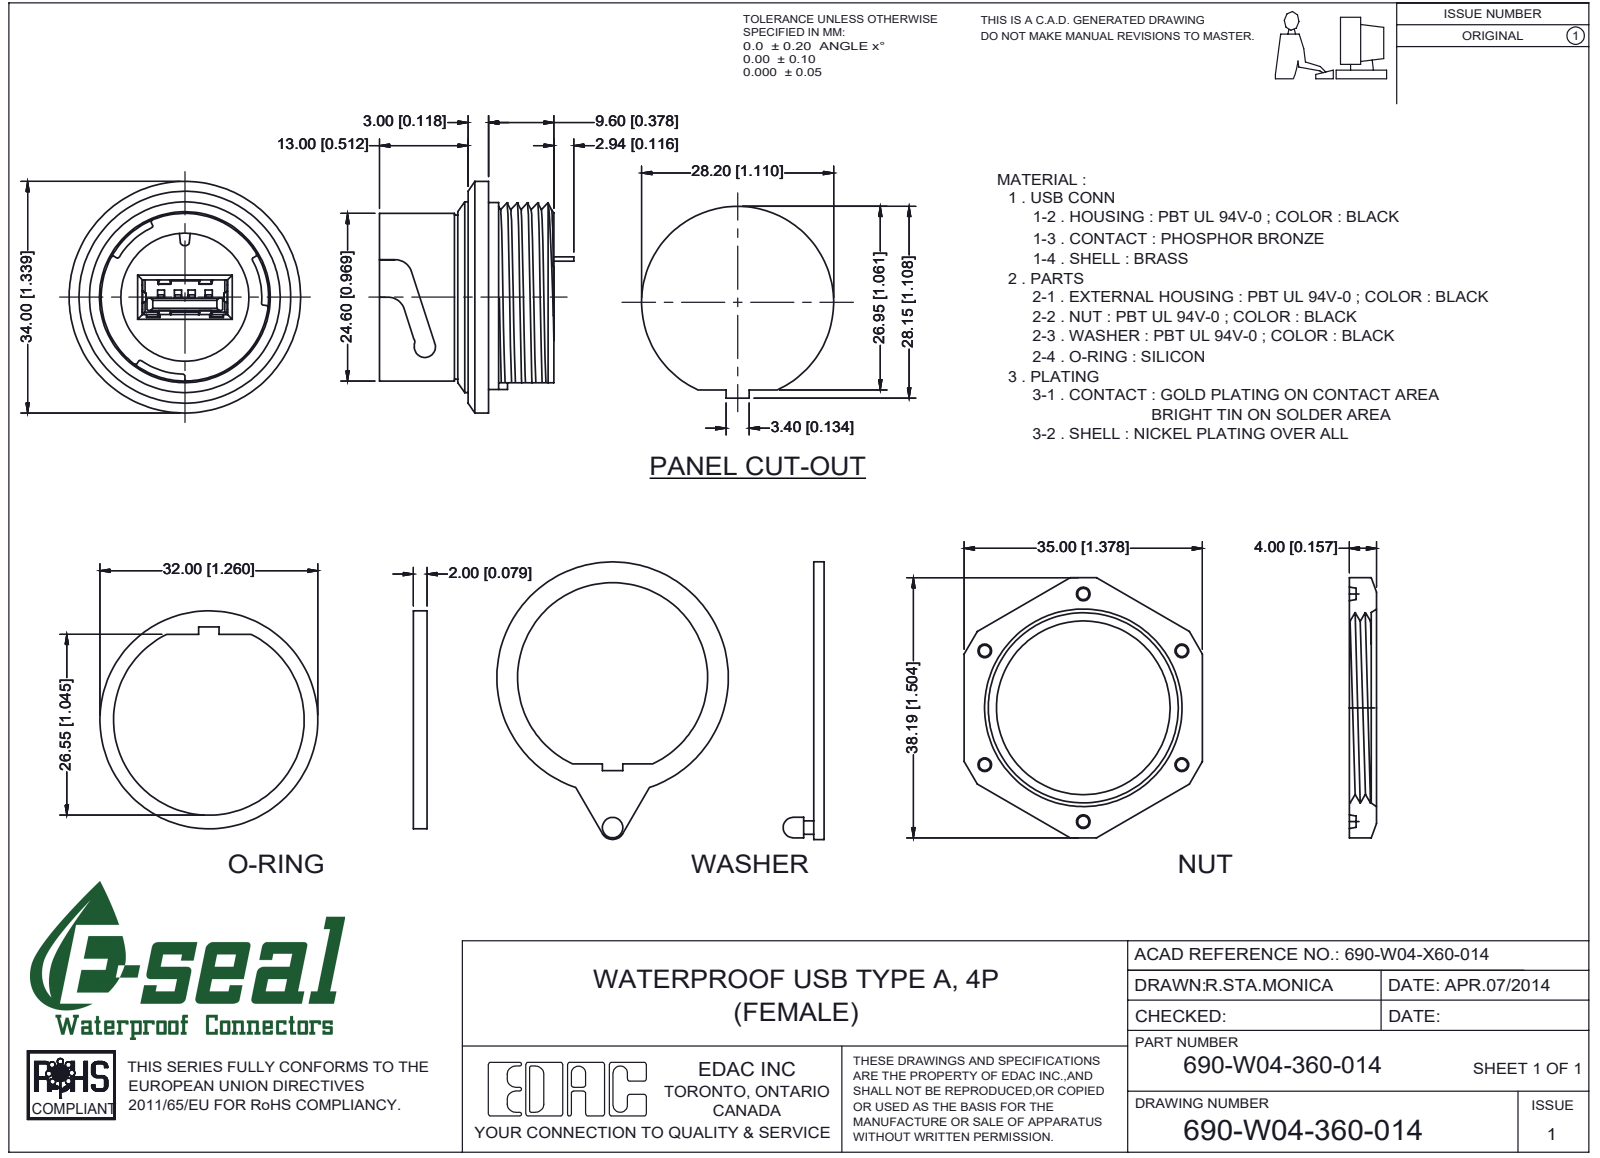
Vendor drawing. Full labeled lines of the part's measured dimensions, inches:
Part name (STEP PRODUCT): USB ASSY 690-W04-X60-014; USB SHELL 690-W04-X60-014; HOUSING 690-W04-X60-014; USB HOUSING (+7 more)
STEP written by: SolidWorks 2020 (AUTOMOTIVE_DESIGN)
Units: inches
Bodies: 23 solids, 1045 faces (734 planar, 252 cylindrical, 59 other)
Overall size (bounding box): 1.667 × 1.339 × 1.124
Volume: 0.612 in³ · Surface area: 20.4 in²
Round holes (diameter × count): ⌀0.039 ×10, ⌀0.74 ×1, ⌀0.827 ×1, ⌀1.063 ×1, ⌀1.098 ×1, ⌀1.102 ×1
Round bosses / shafts (diameter × count): ⌀1.339 ×1, ⌀1.26 ×1, ⌀1.094 ×1, ⌀0.969 ×1, ⌀0.949 ×1, ⌀0.819 ×1, ⌀0.118 ×1, ⌀0.079 ×1
Partial cylindrical surfaces — rounded edges, fillets, slot ends (radius × count): R0.008 ×28, R0.006 ×26, R0.01 ×15, R0.079 ×9, R0.007 ×8, R0.008 ×8, R0.022 ×5, R0.004 ×4
Main face-to-face distances: 0.059, 0.157, 0.22, 0.319, 0.26, 0.118, 0.378, 0.063, 0.043, 0.681
Hole centre spacings: 0.333, 0.1, 0.148, 0.2, 0.276, 0.3, 0.067, 0.068
